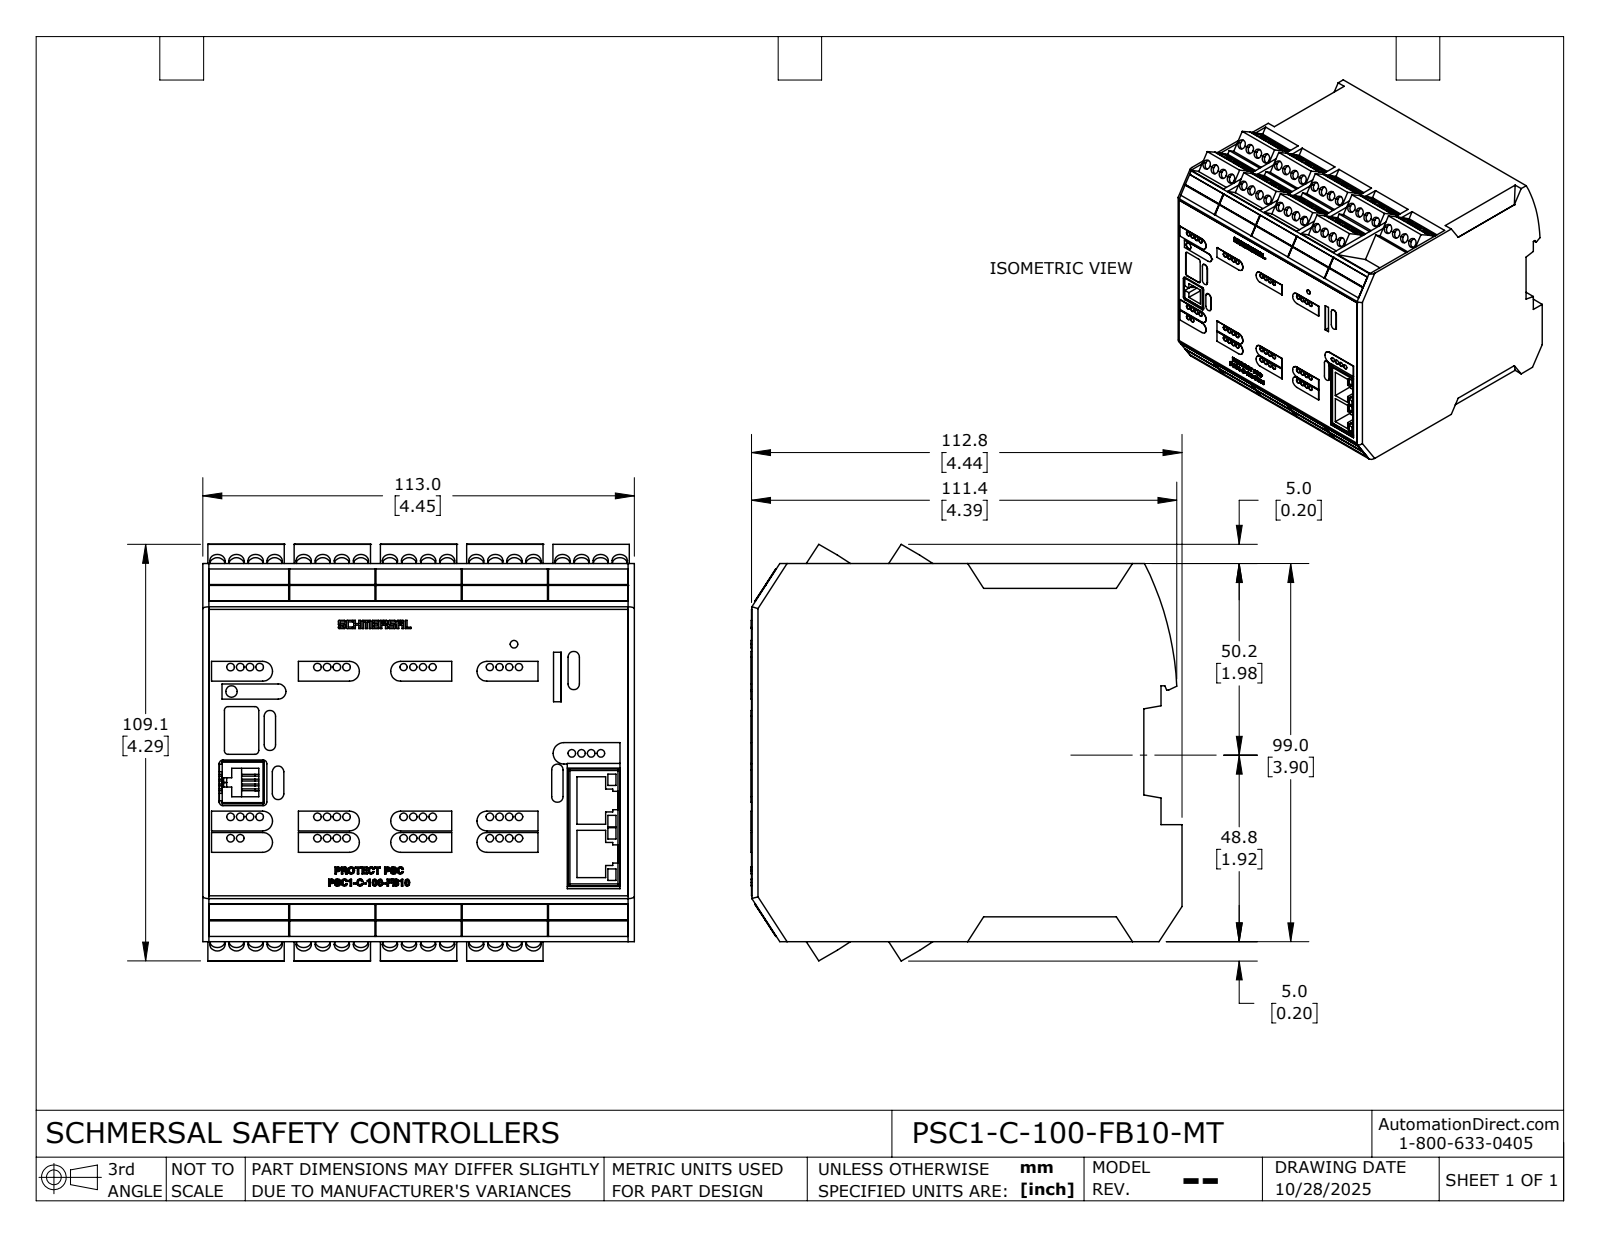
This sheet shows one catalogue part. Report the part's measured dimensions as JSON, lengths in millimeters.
{"part_name": "PSC1-C-100-FB10-MT", "step_written_by": "SolidWorks 2024 (AUTOMOTIVE_DESIGN)", "units": "millimeters", "bodies": {"solids": 1, "faces": 1935, "planar": 1177, "cylindrical": 363, "other": 395}, "overall_size": [113, 112.85, 109.09], "volume_mm3": 1178000, "surface_area_mm2": 92582, "round_holes": [[4, 68], [2, 42], [1.89, 8], [3, 1]], "round_bosses_or_shafts": [[2, 1]], "partial_cylinders_radius": [[2.6, 12], [1, 10], [1.5, 10], [0.3, 8], [0.45, 8], [1.6, 6], [0.7, 4], [0.2, 2]], "face_to_face_distances": [113, 22.6, 99, 45.2, 2.55, 22.55, 20.05, 22.65, 42.65, 67.8], "hole_center_spacings": [22.6, 25.48, 5, 12.78, 27.6, 17.6, 21.17, 30]}
